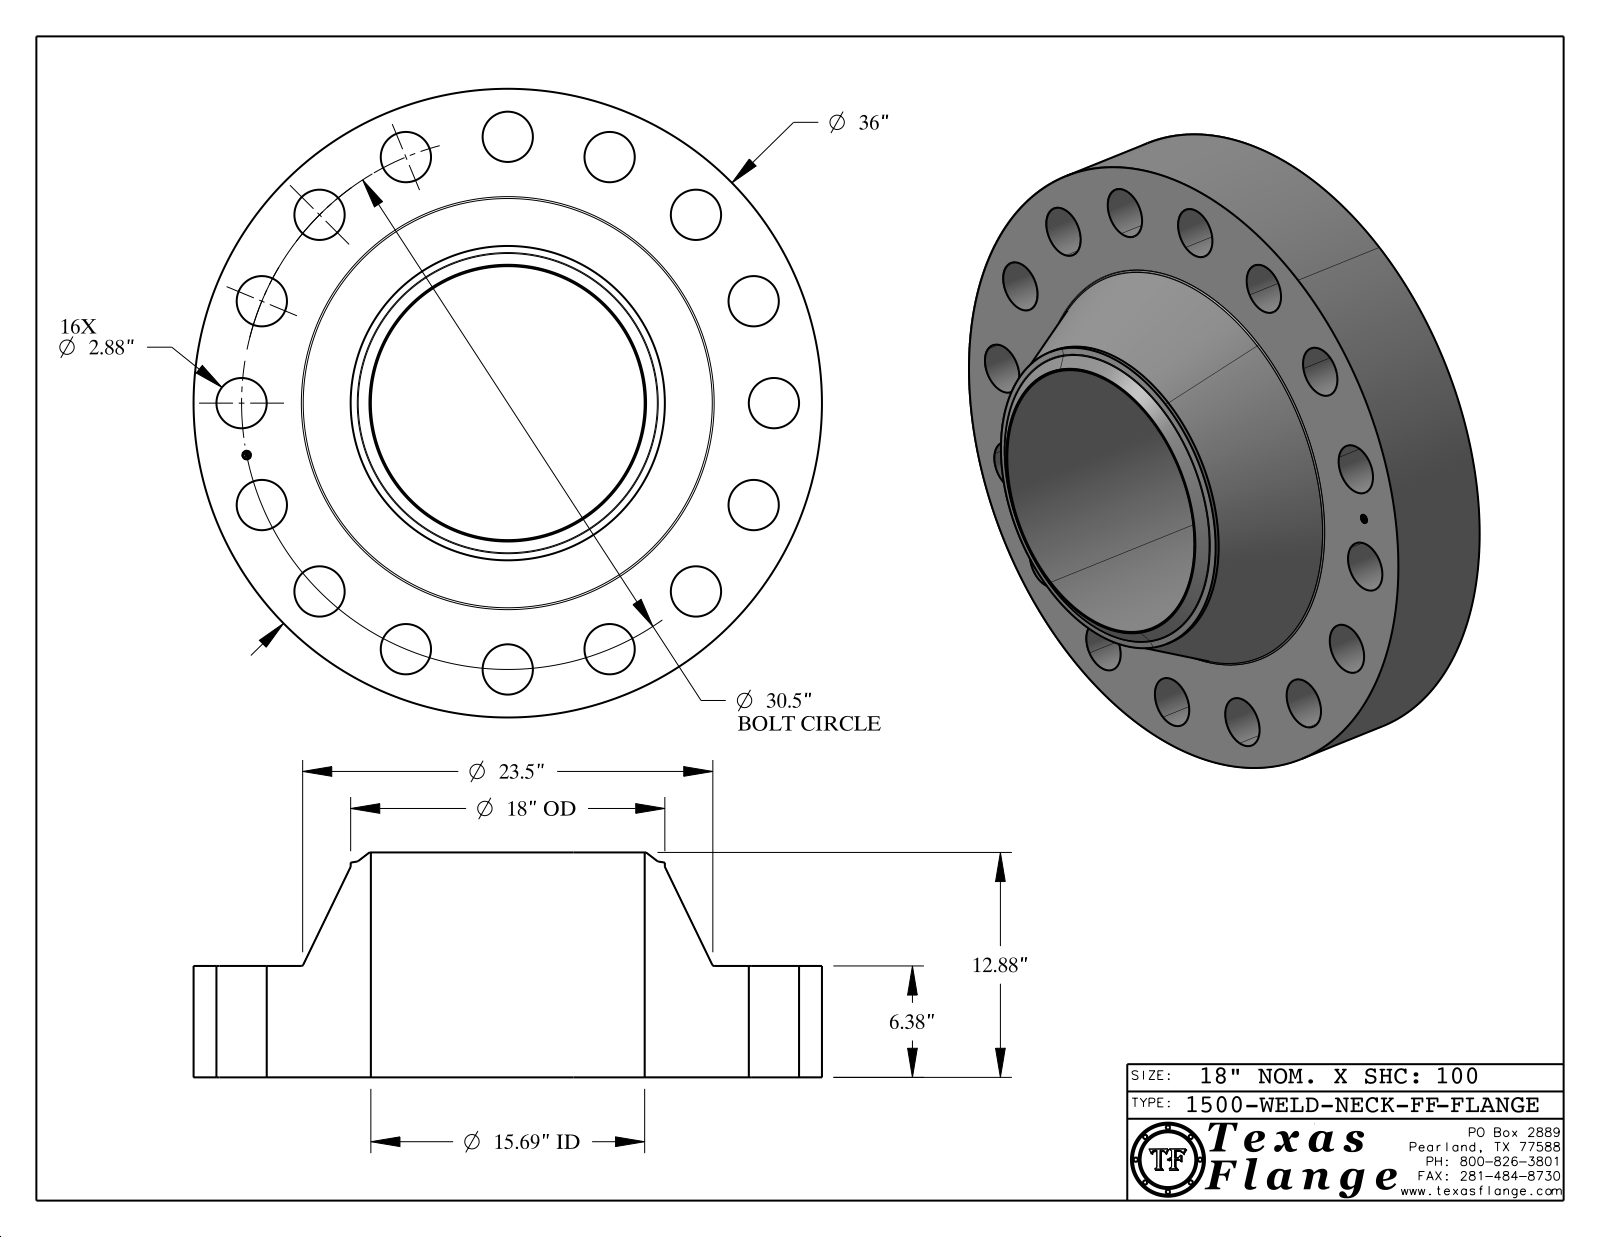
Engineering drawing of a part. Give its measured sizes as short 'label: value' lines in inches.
name: 1500-WELD-NECK-FF
written by: CATIA V5 STEP AP214 (AUTOMOTIVE_DESIGN)
unit: in
bodies: 1 solid, 436 faces (368 planar, 58 cylindrical, 10 other)
size: 36 × 36 × 12.88
volume: 5 459 in³; area: 3 974 in²
holes: 16× ⌀2.88, 1× ⌀0.495, 1× ⌀15.688
bosses: 8× ⌀0.03, 1× ⌀36, 1× ⌀18, 1× ⌀0.39
face distances: 6.38, 12.88, 6.5, 6.365, 0.015, 6.515, 0.148, 0.145, 0.027, 0.096
hole spacings: 5.95, 16.945, 29.914, 15.25, 11.672, 11.672, 15.25, 21.567
